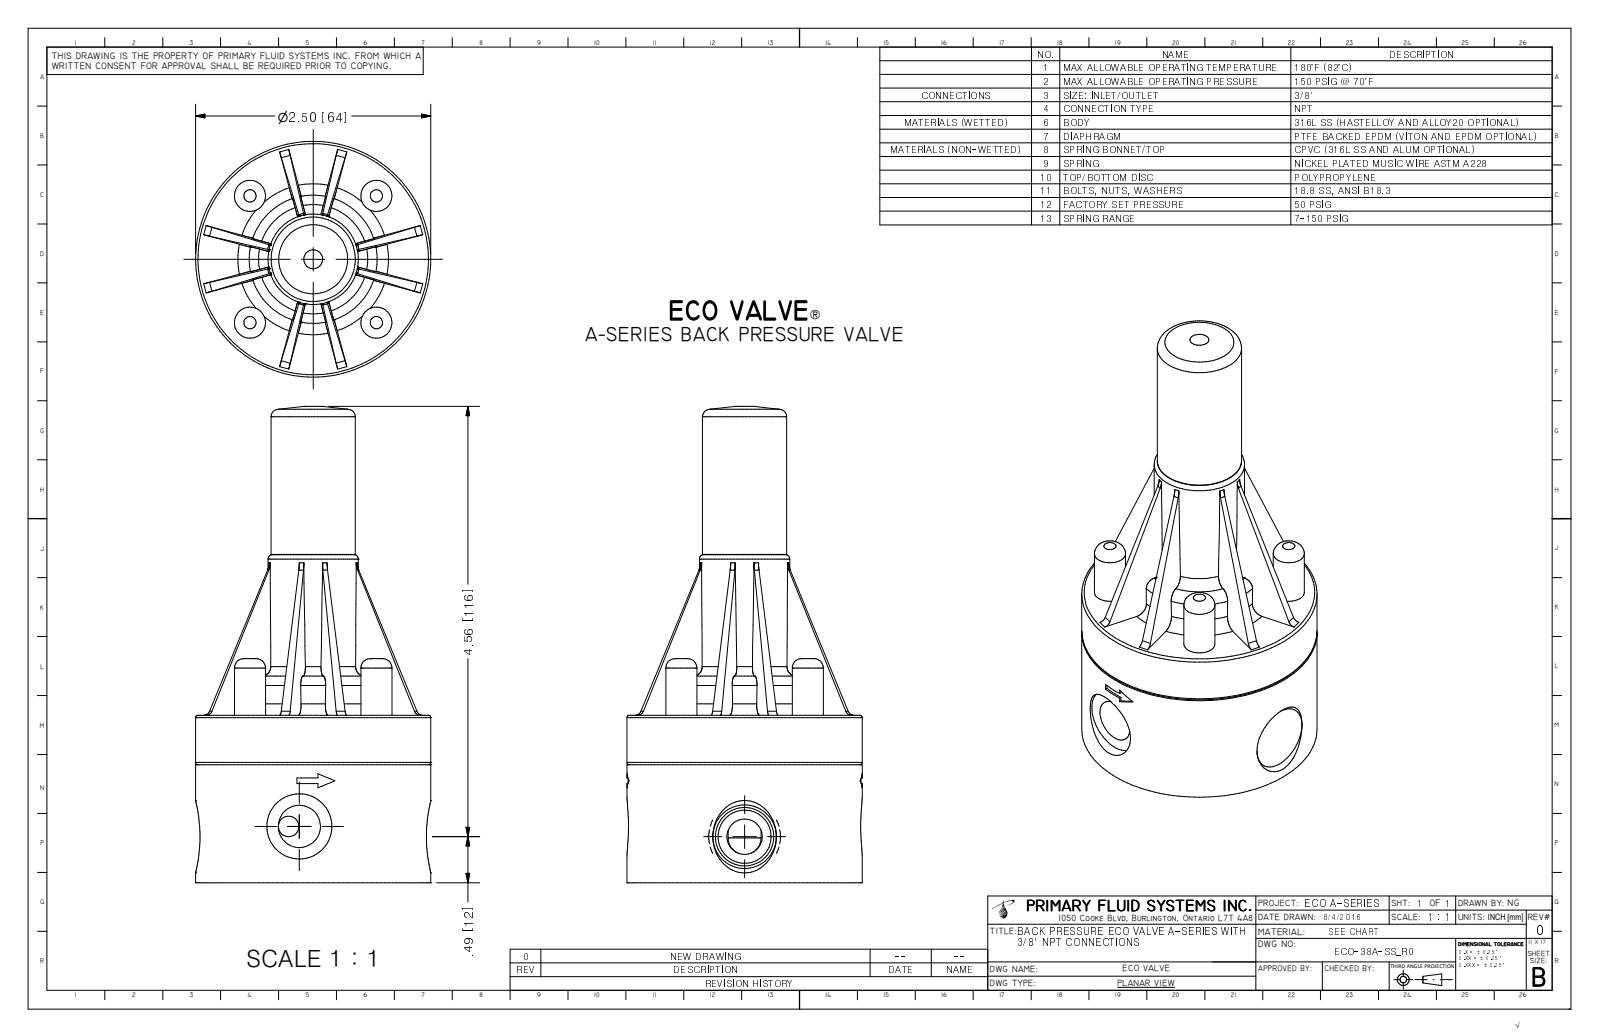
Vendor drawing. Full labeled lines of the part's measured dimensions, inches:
Part name (STEP PRODUCT): ECO-38A-SS_R0
STEP written by: Autodesk Inventor 2009 (AUTOMOTIVE_DESIGN)
Units: inches
Bodies: 1 solid, 208 faces (97 planar, 50 cylindrical, 61 other)
Overall size (bounding box): 5.051 × 2.5 × 2.5
Volume: 11.06 in³ · Surface area: 56.2 in²
Round holes (diameter × count): ⌀0.23 ×4, ⌀0.257 ×4, ⌀0.4 ×4, ⌀0.218 ×1, ⌀0.448 ×1, ⌀0.691 ×1
Round bosses / shafts (diameter × count): ⌀0.33 ×4, ⌀0.256 ×4, ⌀2.5 ×1, ⌀1.36 ×1, ⌀0.96 ×1, ⌀0.895 ×1
Partial cylindrical surfaces — rounded edges, fillets, slot ends (radius × count): R0.07 ×8, R0.128 ×4, R1.23 ×1
Main face-to-face distances: 1.776, 0.27, 1.408, 1.506, 0.275, 1.501, 0.15, 0.12, 0.125, 1.626
Hole centre spacings: 1.344, 1.901, 1.344, 1.344, 0.114, 1.9, 1.902
